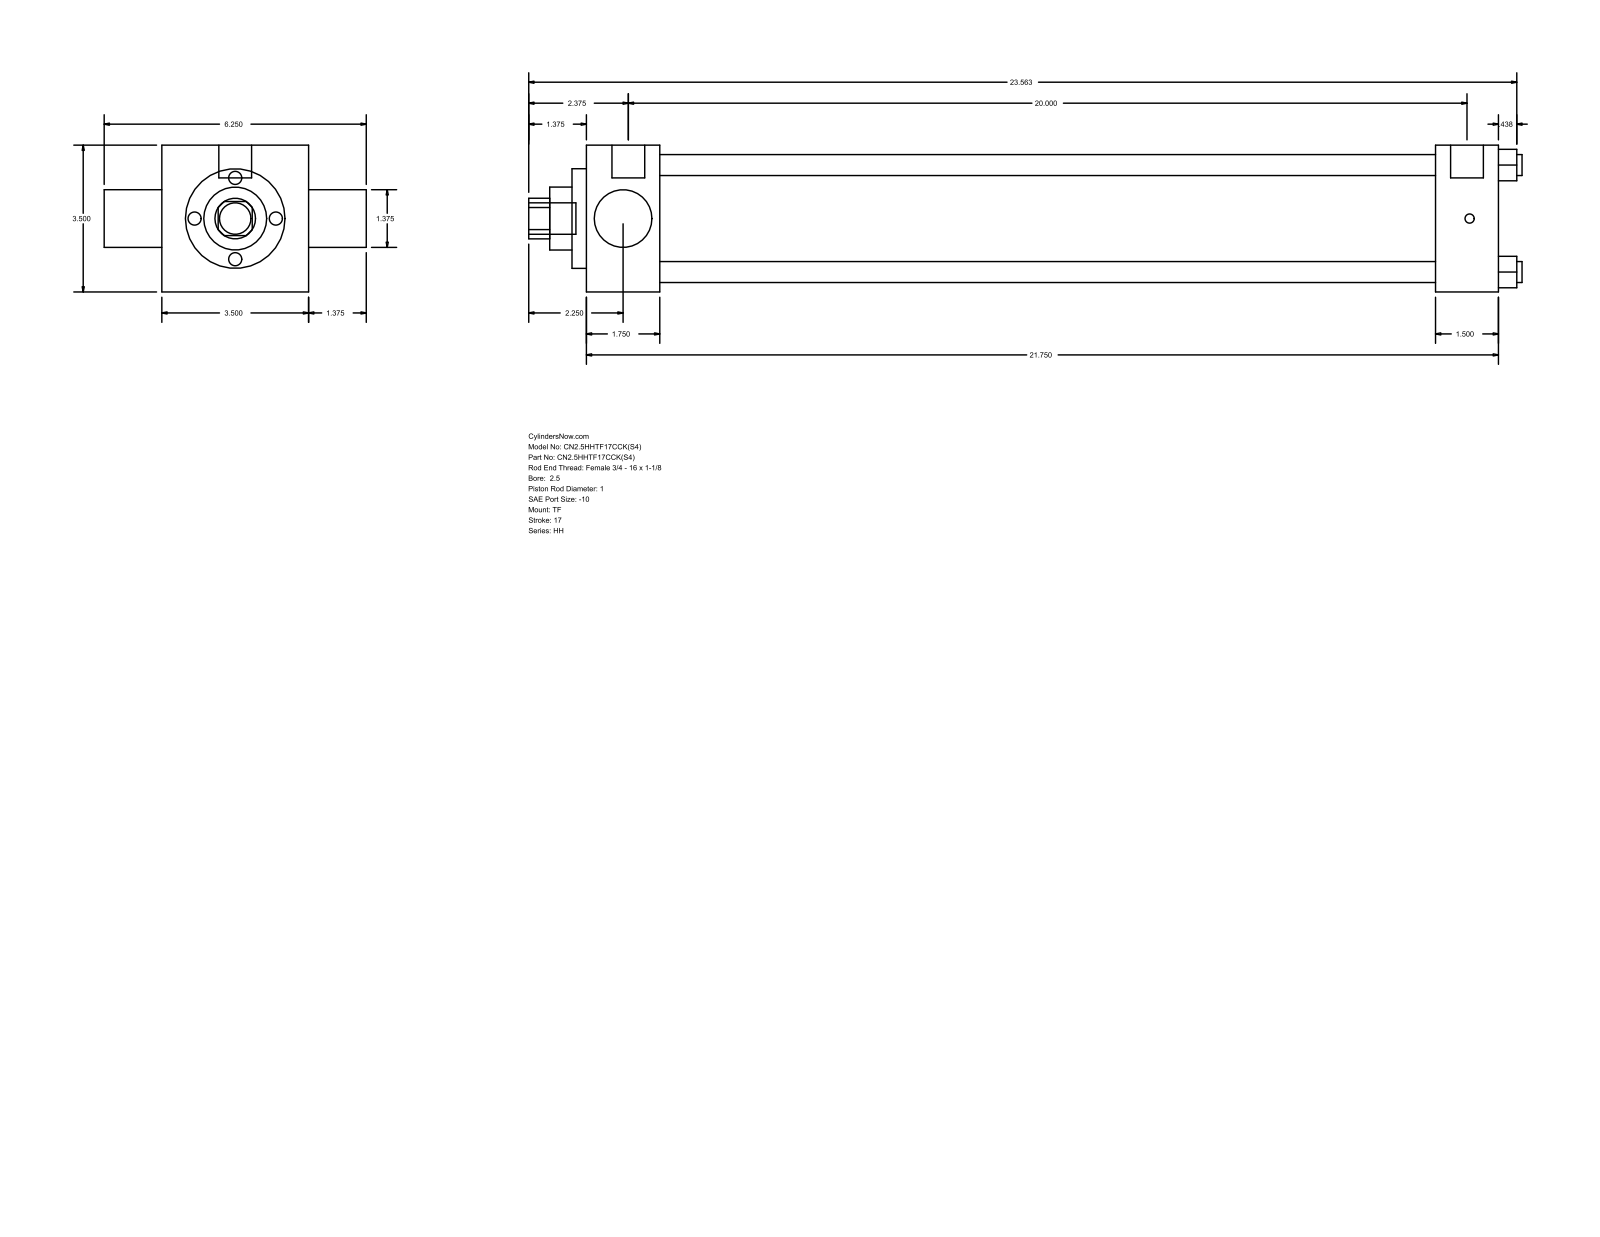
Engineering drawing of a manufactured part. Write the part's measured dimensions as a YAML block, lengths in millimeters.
part_name: "HH_TF__0250_1"
step_written_by: "GSSL Pune (CONFIG_CONTROL_DESIGN)"
units: millimeters
bodies: {solids: 0, faces: 86, planar: 61, cylindrical: 25, other: 0}
overall_size: [601.66, 158.75, 88.9]
round_holes:
  - {diameter: 12.7, count: 4}
  - {diameter: 25.4, count: 1}
  - {diameter: 34.92, count: 1}
  - {diameter: 38.1, count: 1}
  - {diameter: 60.33, count: 1}
  - {diameter: 73.03, count: 1}
round_bosses_or_shafts:
  - {diameter: 5.56, count: 3}
  - {diameter: 19.84, count: 2}
  - {diameter: 19.05, count: 1}
partial_cylinders:
  - {radius: 12.29, count: 1}
face_to_face_distances: [88.9, 552.46, 44.46, 508, 514.35, 469.89, 38.11, 34.93, 123.83, 8.73]
hole_center_spacings: [45.79, 64.76, 91.58]
